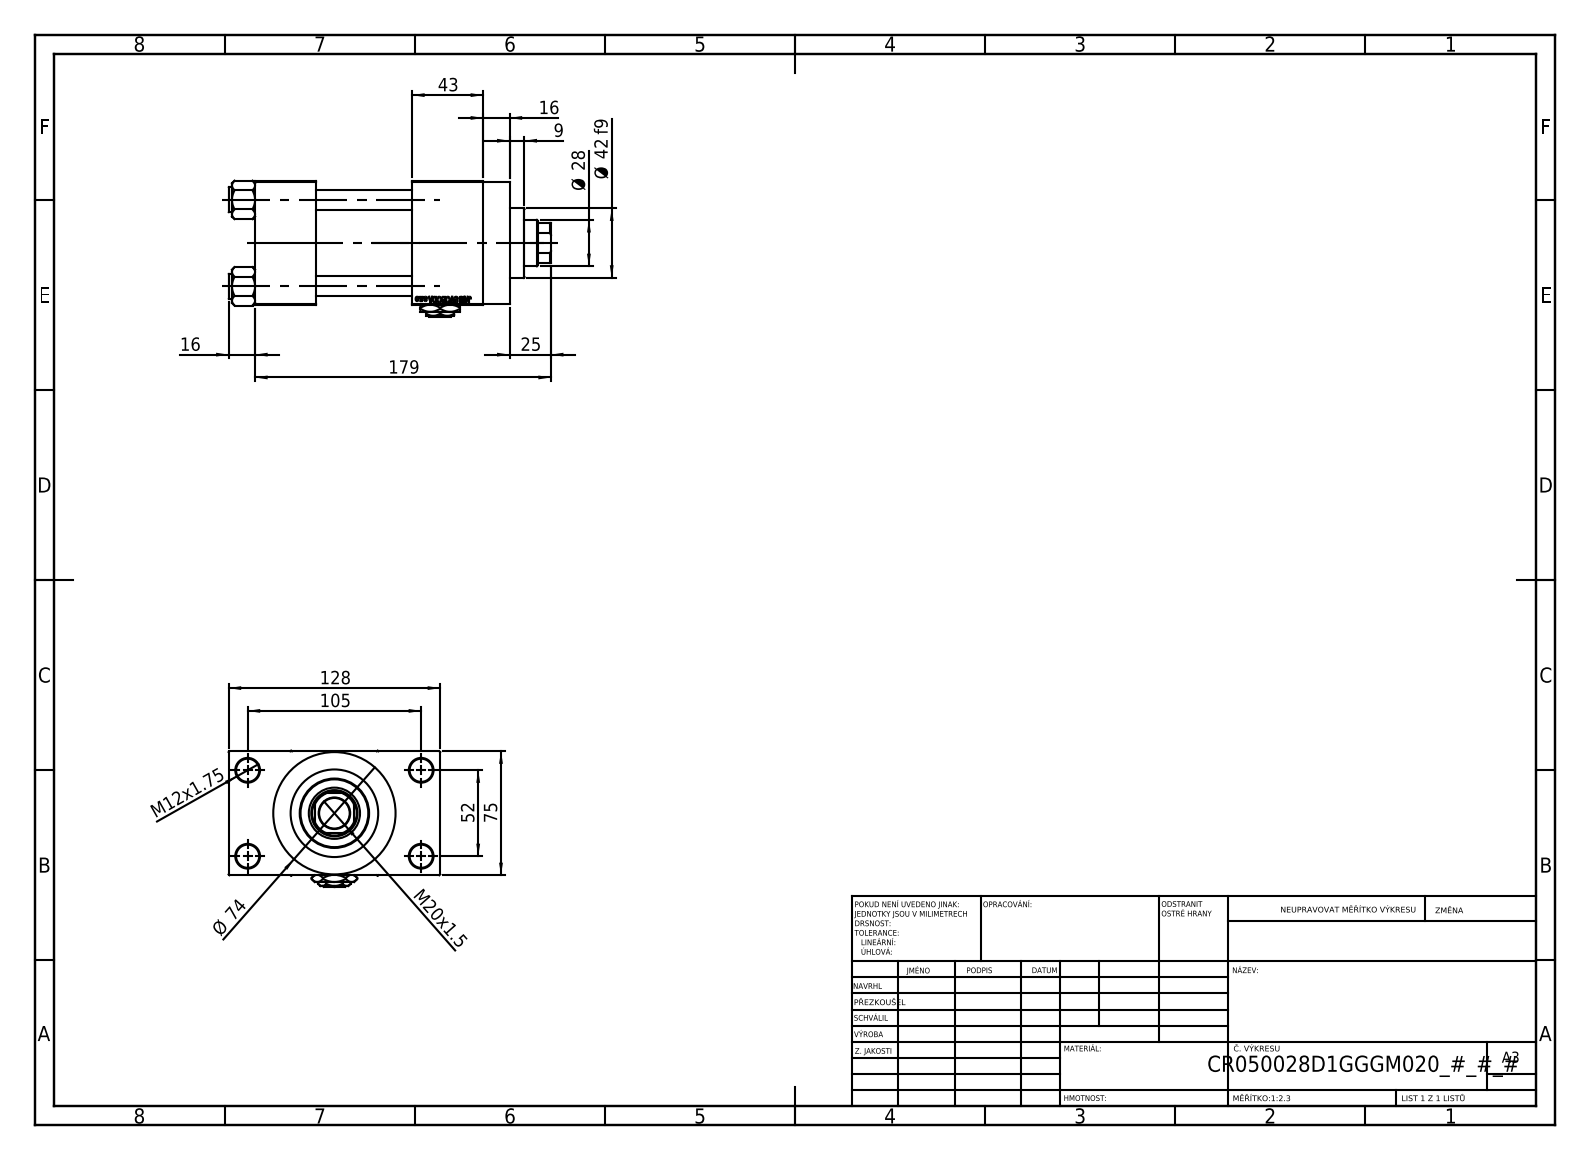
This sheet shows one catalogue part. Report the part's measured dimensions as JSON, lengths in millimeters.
{"part_name": "V215_VC_A; V215CR_VCP_D; V215CR_D_TYCINKA; Zatka_pro_OIL_PORT (+2 more)", "step_written_by": "SolidWorks 2019 (CONFIG_CONTROL_DESIGN)", "units": "millimeters", "bodies": {"solids": 12, "faces": 1152, "planar": 521, "cylindrical": 93, "other": 538}, "overall_size": [195, 128, 82.27], "volume_mm3": 813017, "surface_area_mm2": 170496, "round_holes": [[12, 4], [14, 4], [7, 2], [20.96, 2], [30, 2], [18.5, 1], [28, 1], [31, 1], [41, 1], [50, 1], [53, 1]], "round_bosses_or_shafts": [[15, 4], [74, 1], [56, 1], [42, 1]], "partial_cylinders_radius": [[13.5, 1]], "face_to_face_distances": [75, 58, 37, 95, 26.5, 101.5, 138, 101, 43, 16], "hole_center_spacings": [26.35, 36.98, 52.3, 58.43, 58.59, 78.65, 94.37, 52]}
